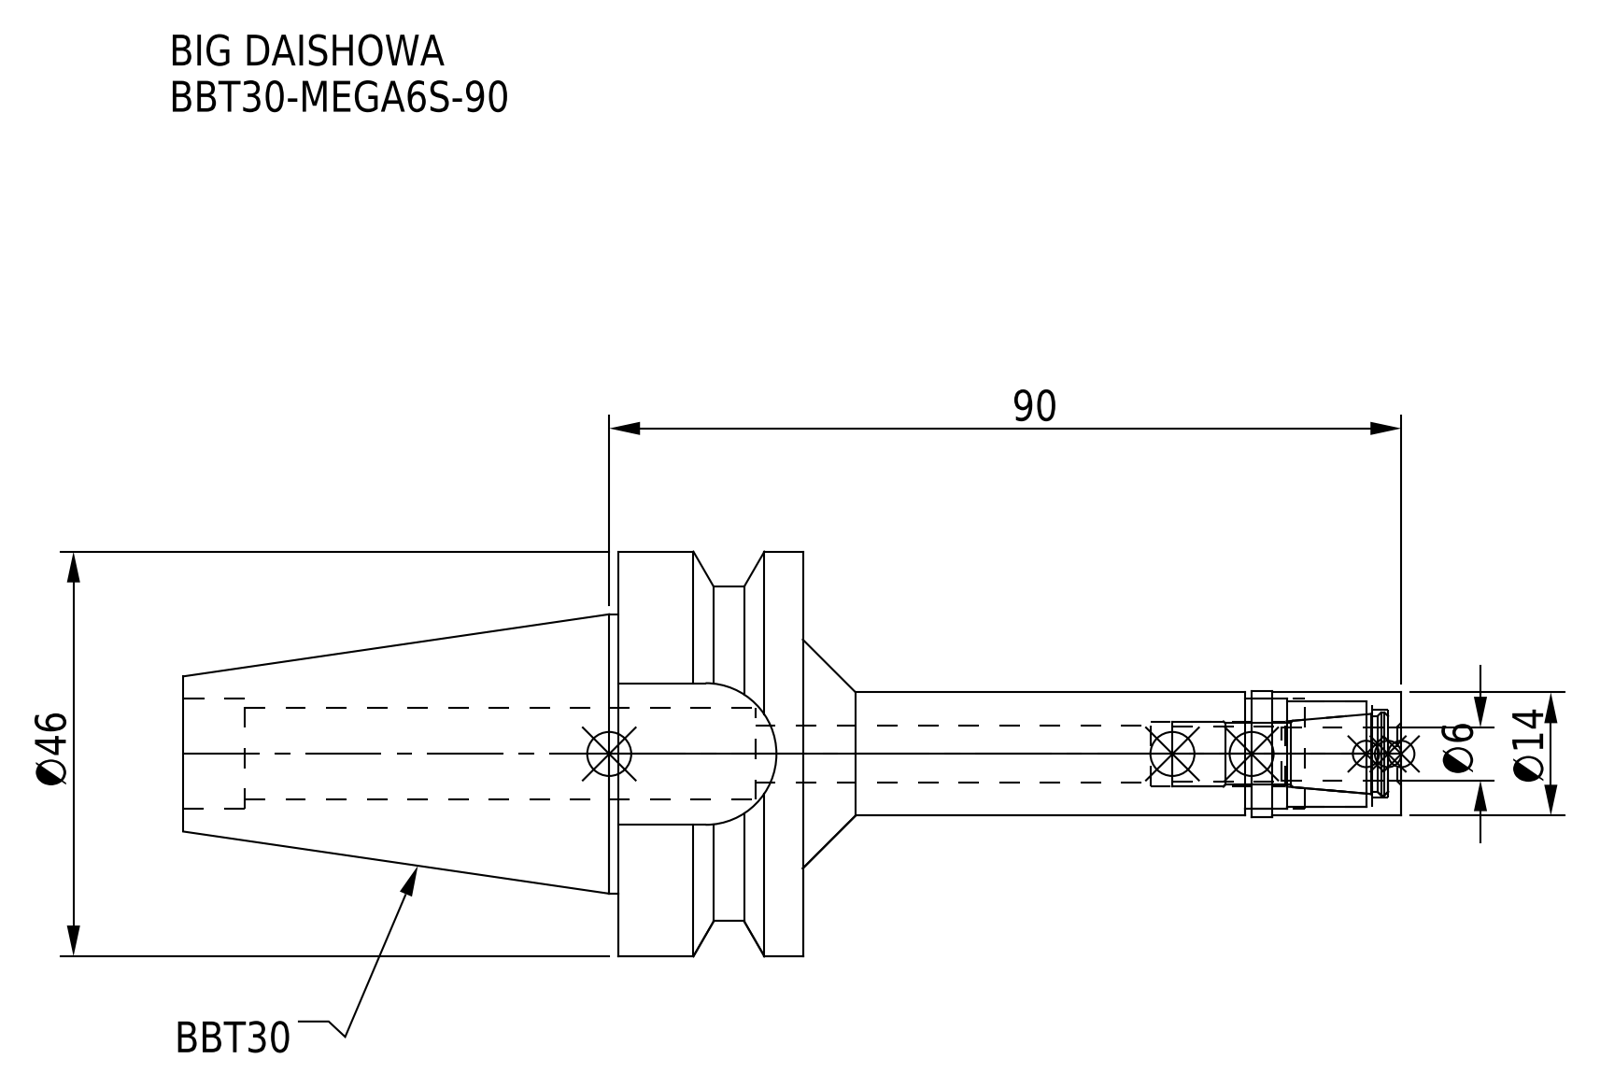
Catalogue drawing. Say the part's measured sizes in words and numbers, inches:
The part is named "BBT30-MEGA6S-90; MGN6S_1.stp; BBT30MS06090-060_ASM.stp; BBT30-MEGA6S-90_1.stp (+3 more)". Its 3-D file was written by "SolidWorks 2019 (CONFIG_CONTROL_DESIGN)". It is 2 solids with 71 faces: 21 planar, 38 cylindrical and 12 other. Overall it measures 5.449 by 1.811 by 1.811 inches. Its volume is 3.457 cubic inches and its surface area 27.99 square inches. Round holes: 1 of diameter 0.24, 1 of diameter 0.252, 1 of diameter 0.291, 1 of diameter 0.394, 1 of diameter 0.409, 1 of diameter 0.472, 1 of diameter 0.492. Round bosses or shafts: 1 of diameter 1.811, 1 of diameter 1.25, 1 of diameter 0.563, 1 of diameter 0.551, 1 of diameter 0.551, 1 of diameter 0.492, 1 of diameter 0.472. Partial cylindrical surfaces (rounded edges, fillets, slot ends): 1 of radius 0.317, 1 of radius 0.748. The main face-to-face distances are 0.827, 1.283, 2.772, 1.945, 2.677, 3.504, 5.449, 0.634, 0.028, 0.539.
